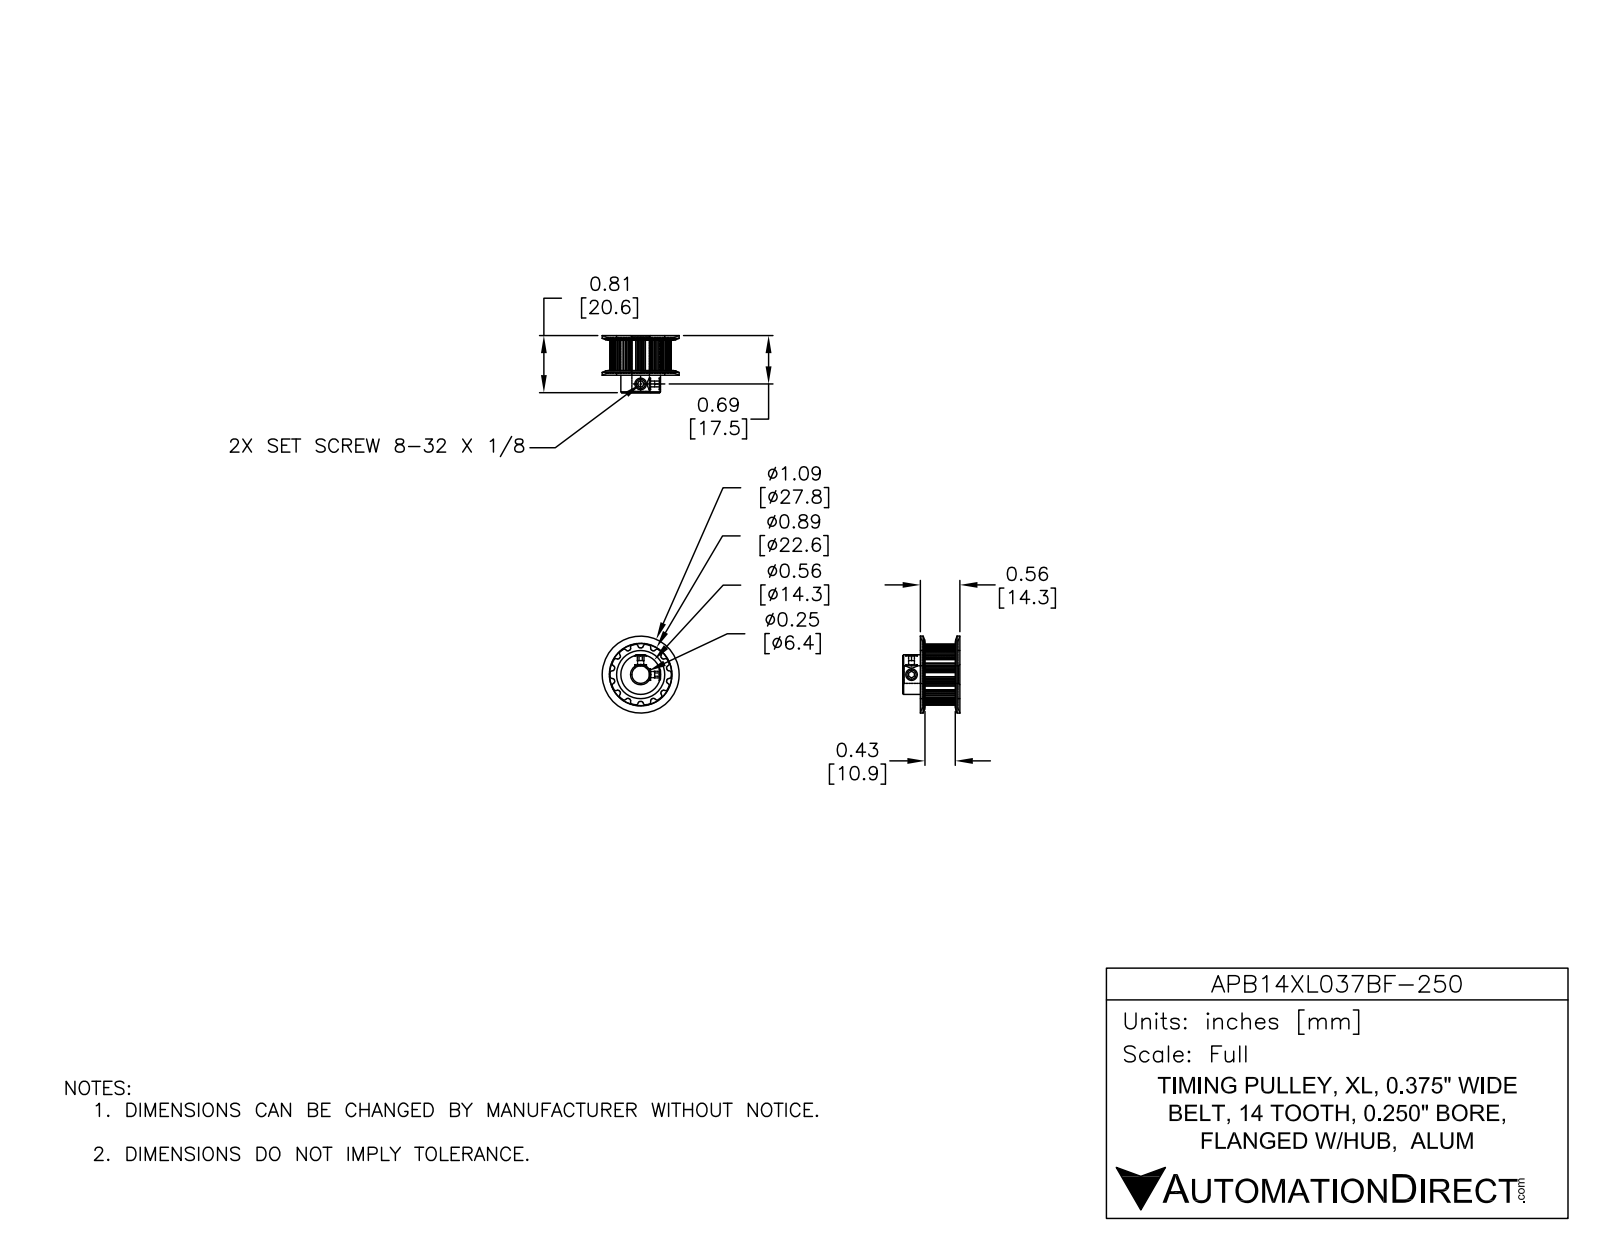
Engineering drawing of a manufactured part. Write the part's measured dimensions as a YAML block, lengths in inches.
part_name: "APB14XL037BF-250"
step_written_by: "SolidWorks 2014 (AUTOMOTIVE_DESIGN)"
units: inches
bodies: {solids: 1, faces: 161, planar: 48, cylindrical: 91, other: 22}
overall_size: [1.094, 1.094, 0.813]
volume: 0.329
surface_area: 5.553
round_holes:
  - {diameter: 0.088, count: 2}
  - {diameter: 0.25, count: 1}
round_bosses_or_shafts:
  - {diameter: 0.563, count: 1}
partial_cylinders:
  - {radius: 0.015, count: 56}
  - {radius: 0.381, count: 1}
face_to_face_distances: [0.495, 0.033, 0.871, 0.528, 0.813, 0.78, 0.285, 0.275, 0.065, 0.032]
